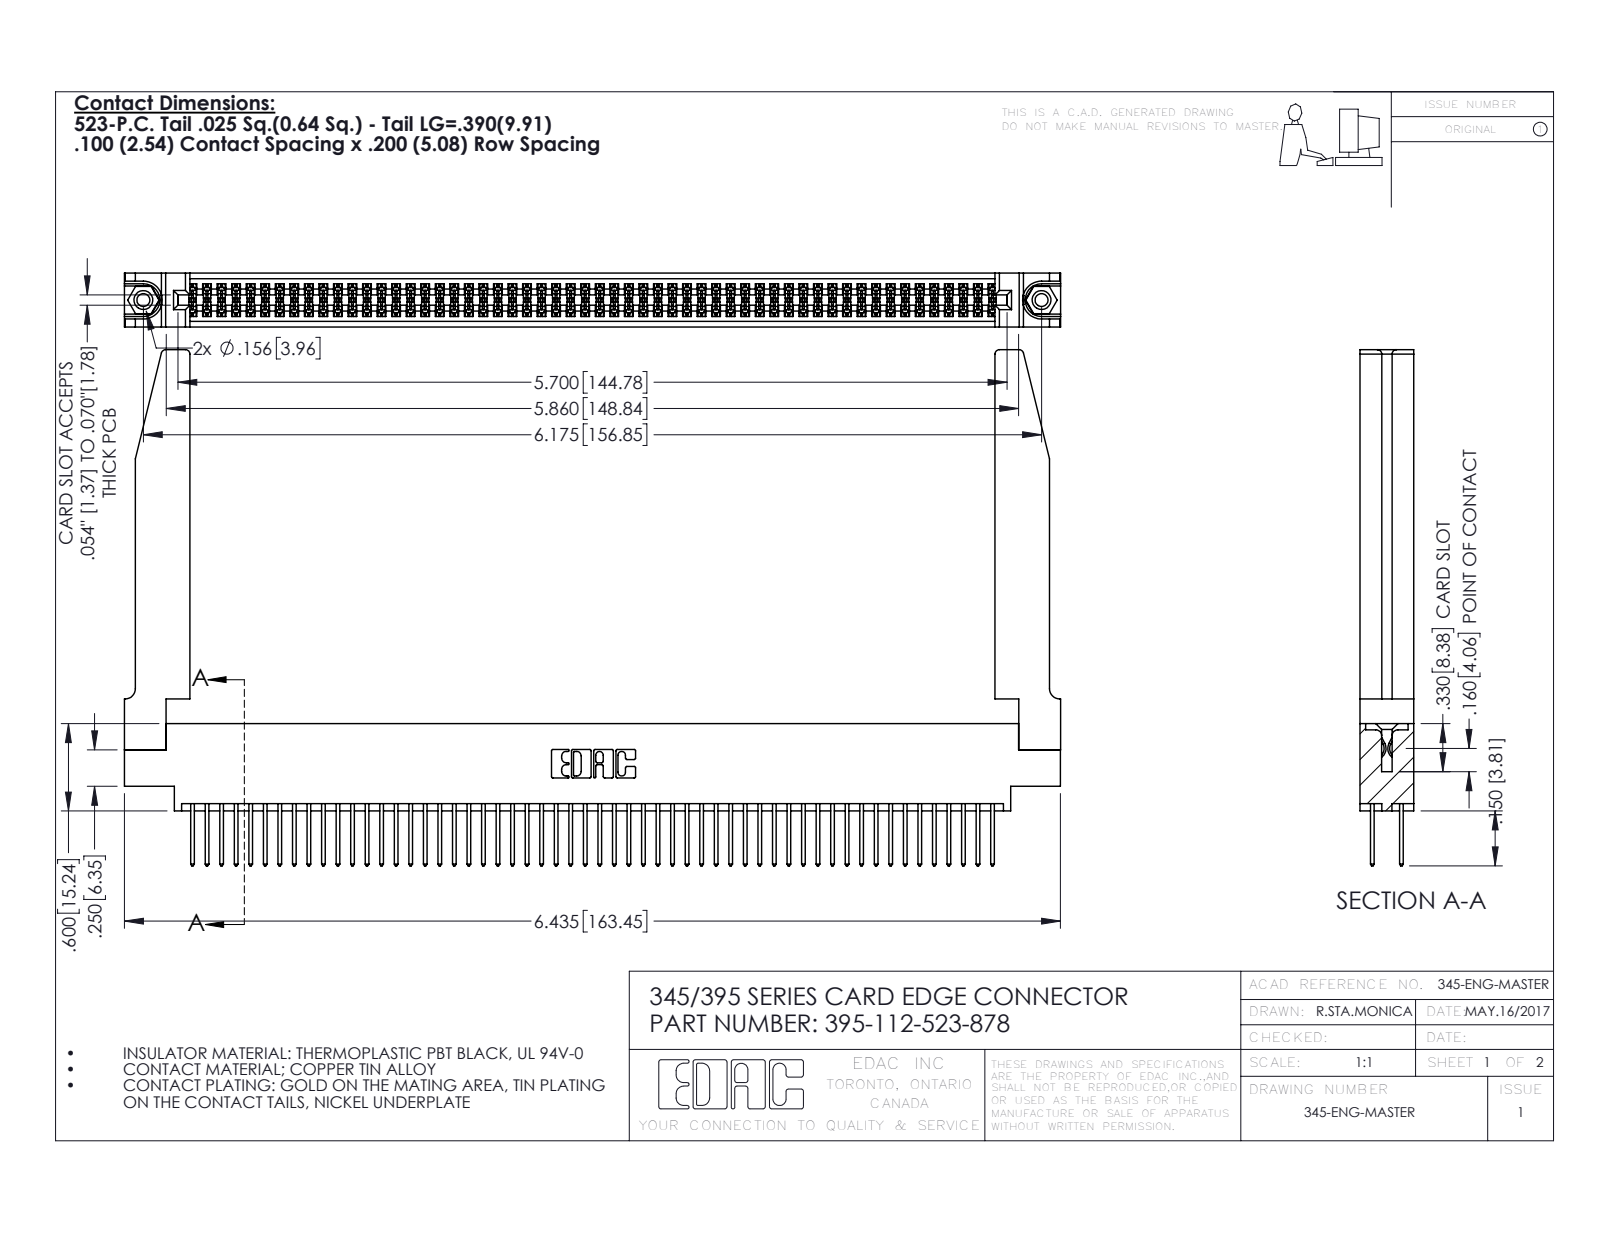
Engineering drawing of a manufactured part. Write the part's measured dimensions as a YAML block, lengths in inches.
part_name: "345-220-078_345-220-078; 345-292-001_345-293-123; 395-112-523-878; 345-250-001_345-250-001-102 (+1 more)"
step_written_by: "SolidWorks 2016 (CONFIG_CONTROL_DESIGN)"
units: inches
bodies: {solids: 117, faces: 5964, planar: 3922, cylindrical: 1990, other: 52}
overall_size: [6.436, 3.547, 0.37]
volume: 1.458
surface_area: 49.79
round_holes:
  - {diameter: 0.089, count: 2}
  - {diameter: 0.125, count: 2}
  - {diameter: 0.156, count: 2}
  - {diameter: 0.064, count: 1}
round_bosses_or_shafts:
  - {diameter: 0.155, count: 2}
partial_cylinders:
  - {radius: 0.006, count: 168}
  - {radius: 0.01, count: 112}
  - {radius: 0.01, count: 22}
  - {radius: 0.03, count: 8}
  - {radius: 0.007, count: 6}
  - {radius: 0.031, count: 6}
  - {radius: 0.026, count: 3}
  - {radius: 0.014, count: 2}
face_to_face_distances: [0.072, 0.298, 0.37, 0.098, 0.272, 0.025, 0.2, 0.225, 0.175, 0.148]
hole_center_spacings: [0.27, 5.939, 6.175]
